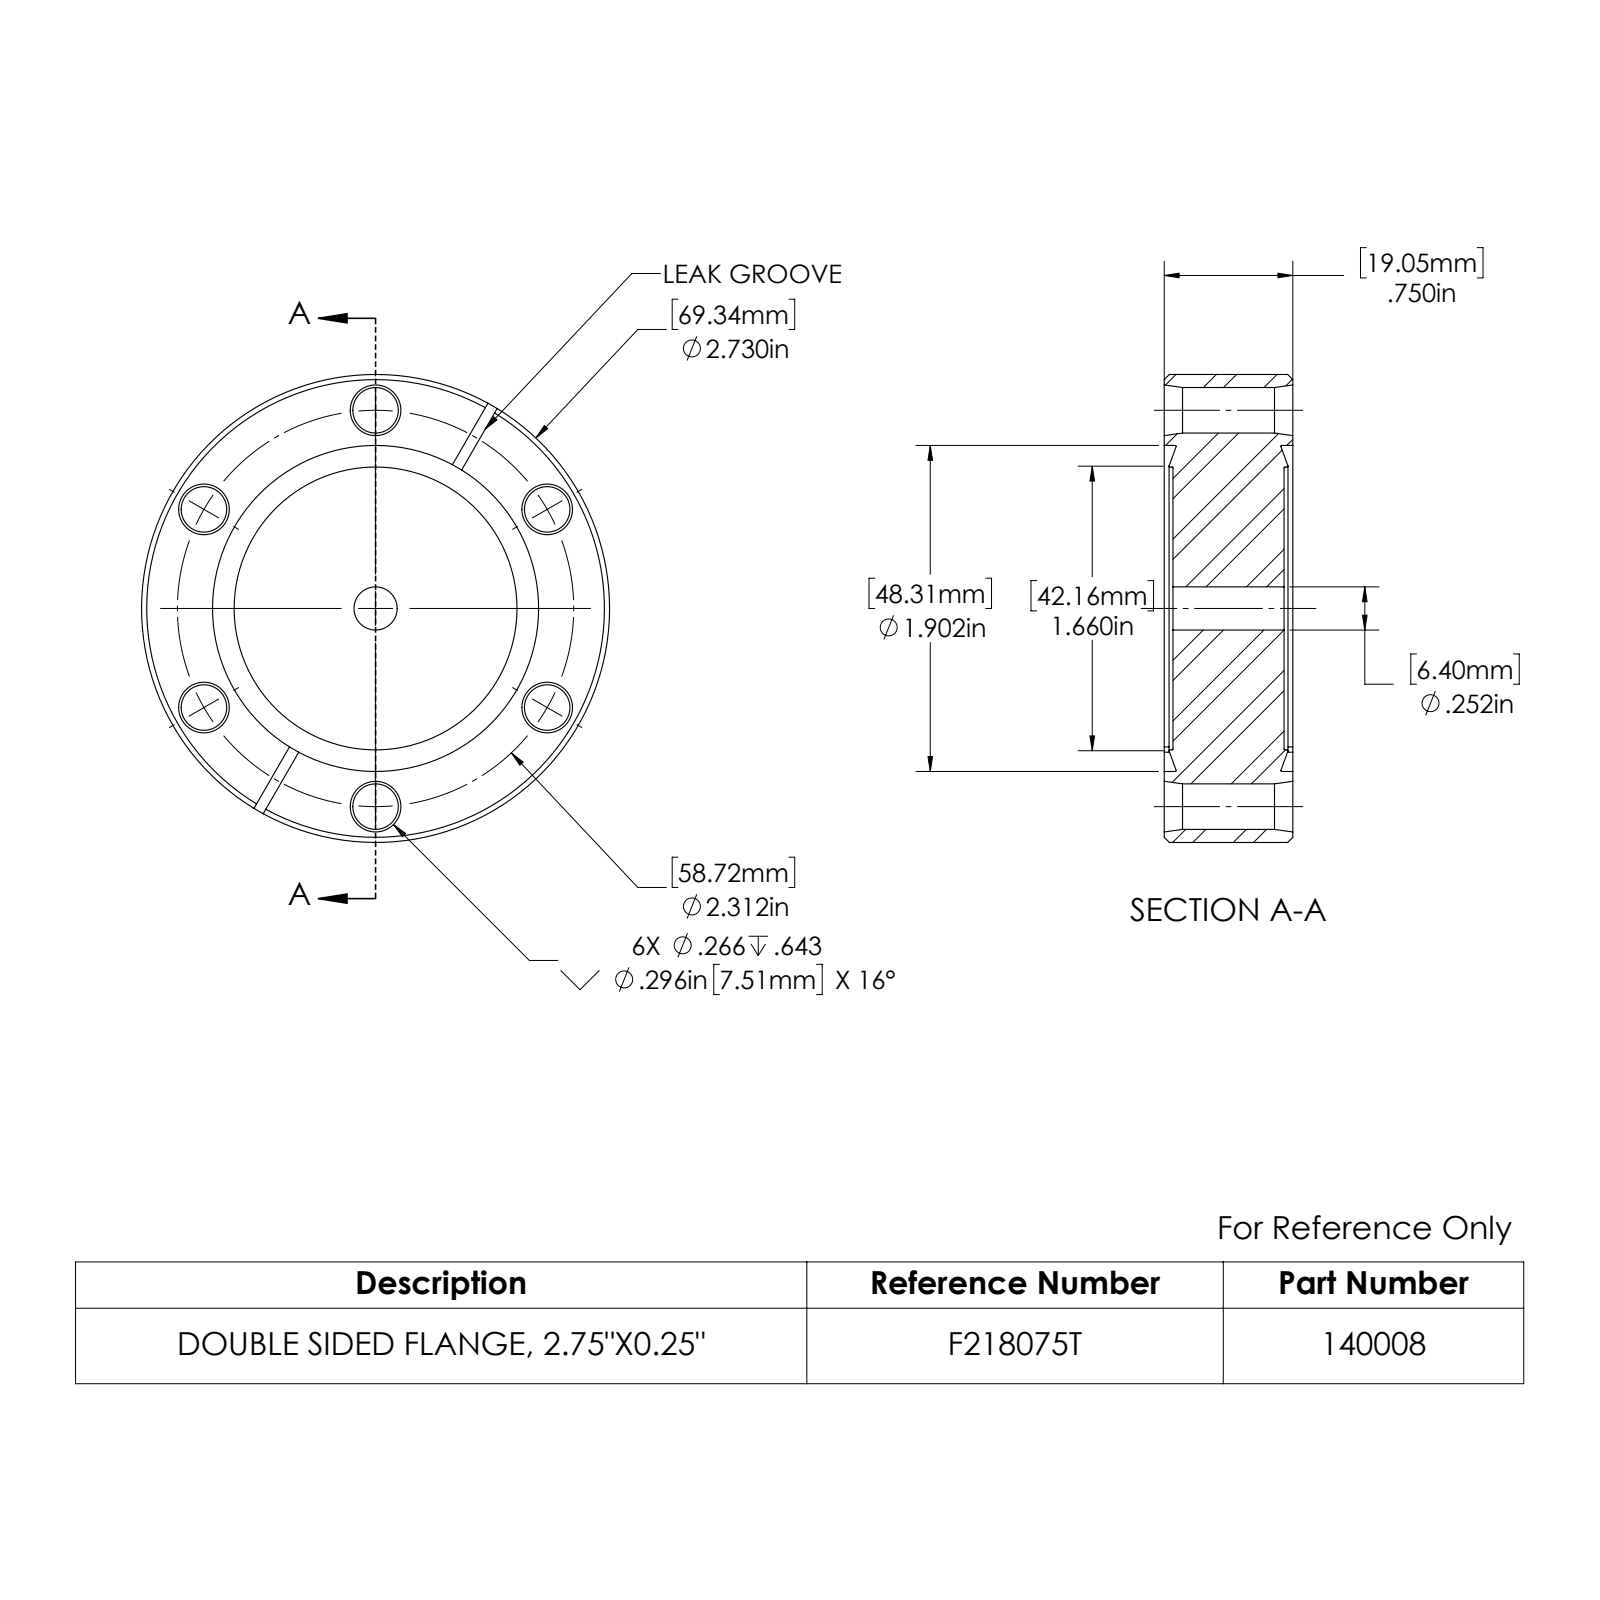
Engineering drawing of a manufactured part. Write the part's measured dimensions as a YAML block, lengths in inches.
part_name: "140008_A"
step_written_by: "SolidWorks 2022 (CONFIG_CONTROL_DESIGN)"
units: inches
bodies: {solids: 1, faces: 88, planar: 14, cylindrical: 28, other: 46}
overall_size: [2.73, 2.73, 0.75]
volume: 3.794
surface_area: 22.65
round_holes:
  - {diameter: 0.266, count: 6}
  - {diameter: 0.252, count: 1}
  - {diameter: 1.65, count: 1}
  - {diameter: 1.902, count: 1}
round_bosses_or_shafts:
  - {diameter: 2.73, count: 1}
partial_cylinders:
  - {radius: 1.25, count: 4}
face_to_face_distances: [0.051, 0.699, 0.75, 0.648, 0.062]
hole_center_spacings: [1.156, 2.002, 2.002, 2.312, 2.312]
